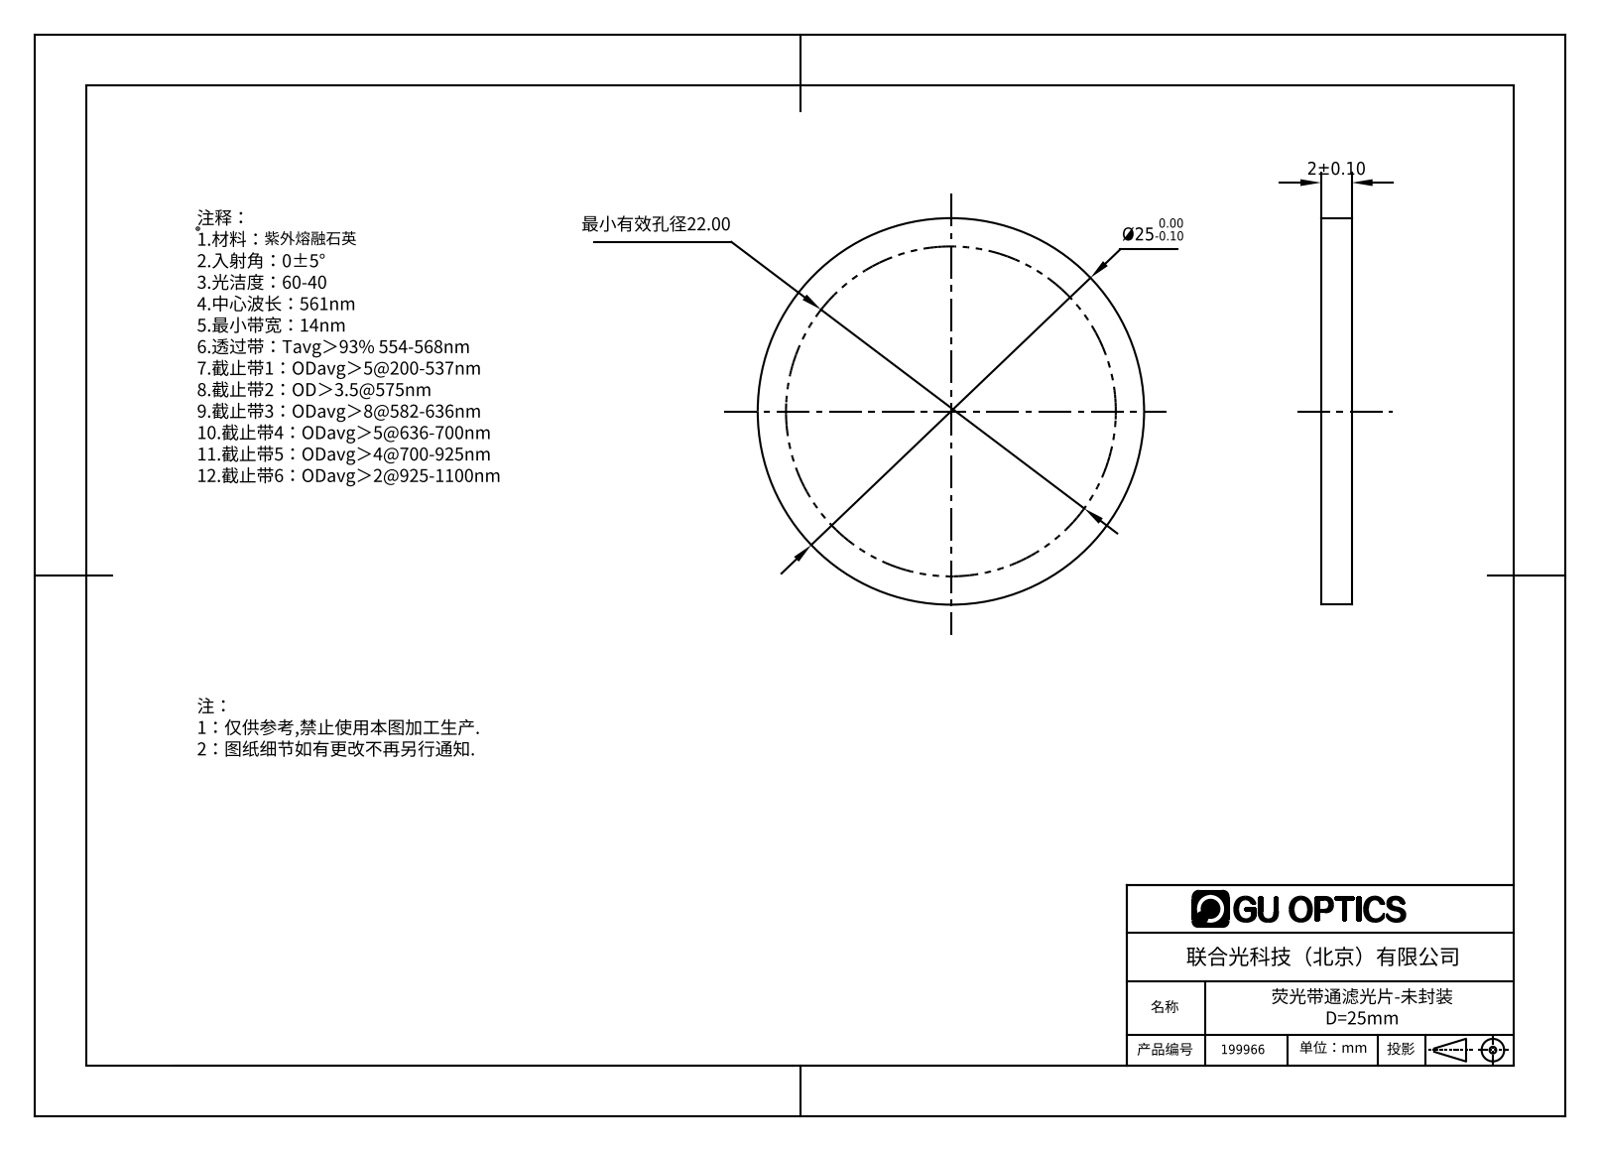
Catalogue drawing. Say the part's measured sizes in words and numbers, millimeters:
The part is named "未封装". Its 3-D file was written by "SolidWorks 2016 (AUTOMOTIVE_DESIGN)". It is 1 solid with 4 faces: 2 planar, 2 cylindrical and 0 other. Overall it measures 25 by 25 by 2 millimeters. Its volume is 982 cubic millimeters and its surface area 1 139 square millimeters. Round bosses or shafts: 1 of diameter 25. The main face-to-face distances are 2.
